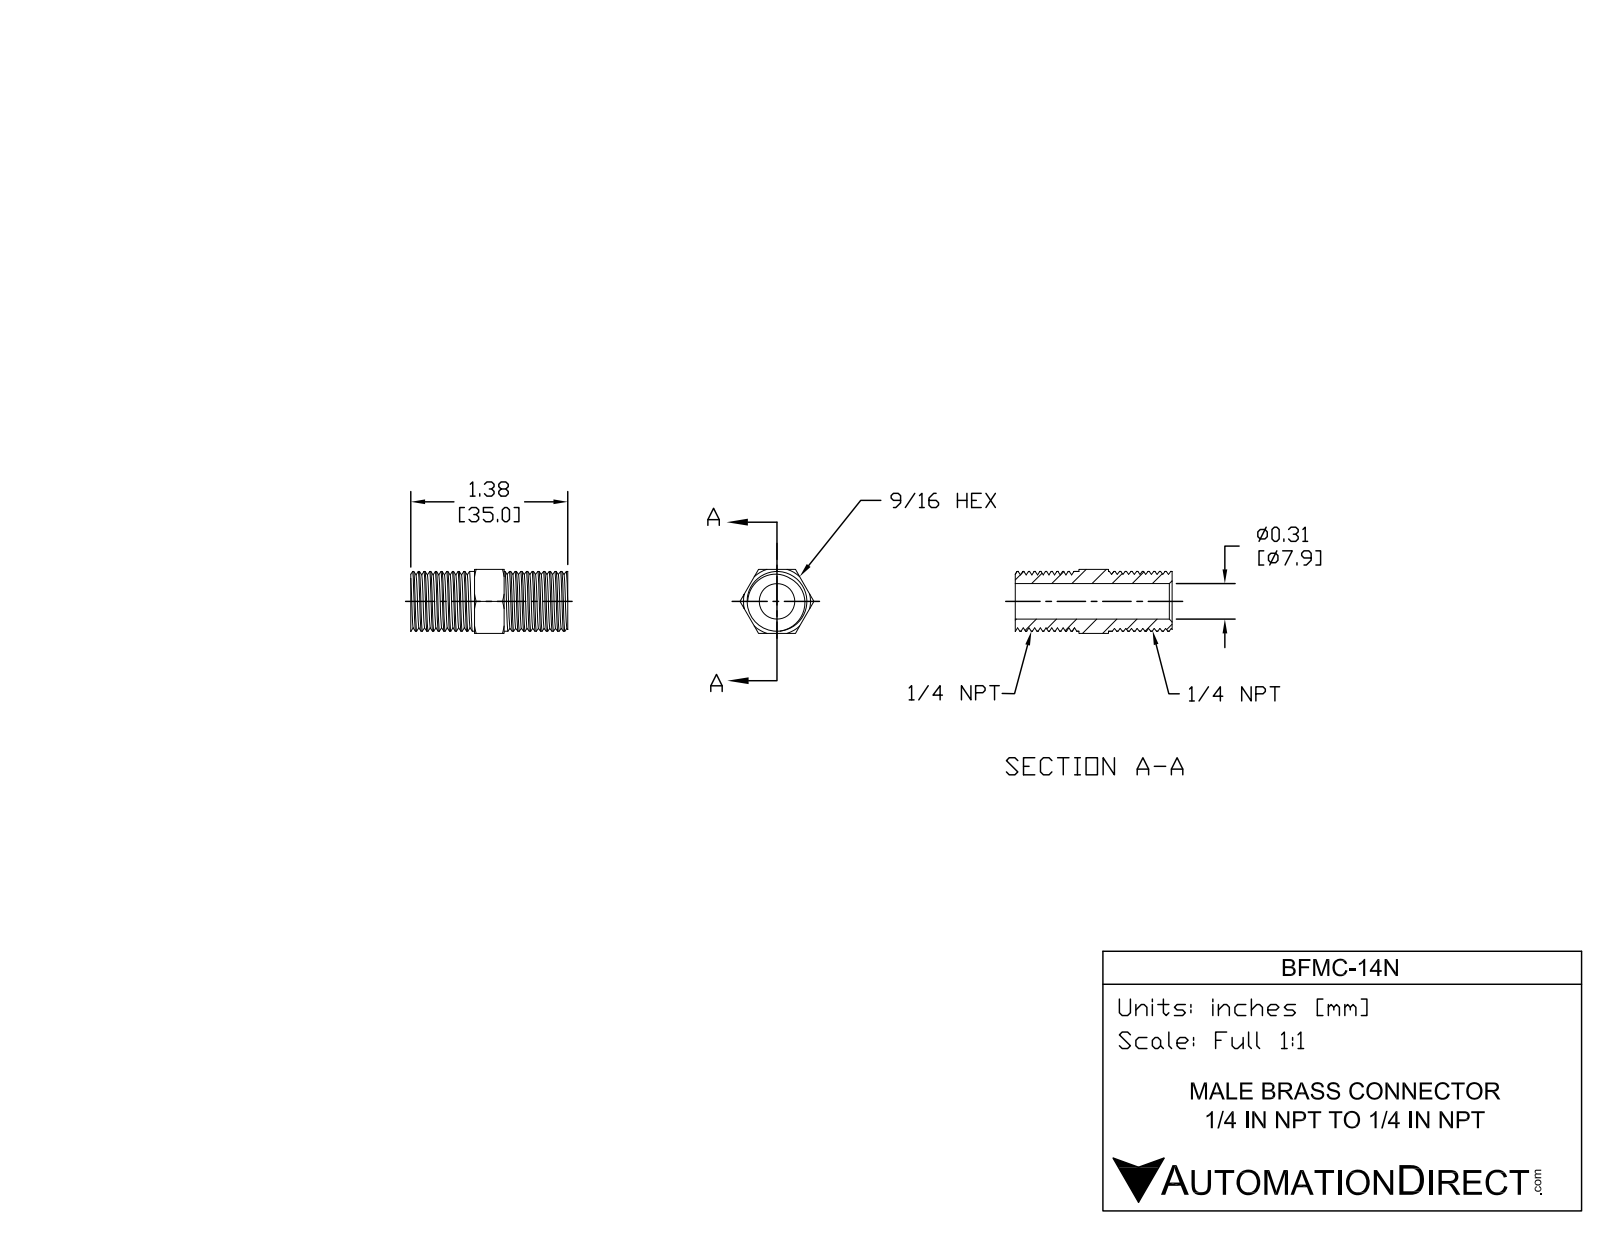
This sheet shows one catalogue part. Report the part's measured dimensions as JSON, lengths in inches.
{"part_name": "BFMC-14N", "step_written_by": "SolidWorks 2015 (CONFIG_CONTROL_DESIGN)", "units": "inches", "bodies": {"solids": 1, "faces": 80, "planar": 13, "cylindrical": 47, "other": 20}, "overall_size": [1.379, 0.65, 0.563], "volume_in3": 0.189, "surface_area_in2": 4.92, "round_holes": [[0.312, 1]], "round_bosses_or_shafts": [[0.525, 1]], "face_to_face_distances": [0.562, 1.379, 0.56, 0.819, 0.82, 0.26, 0.559, 0.281]}
